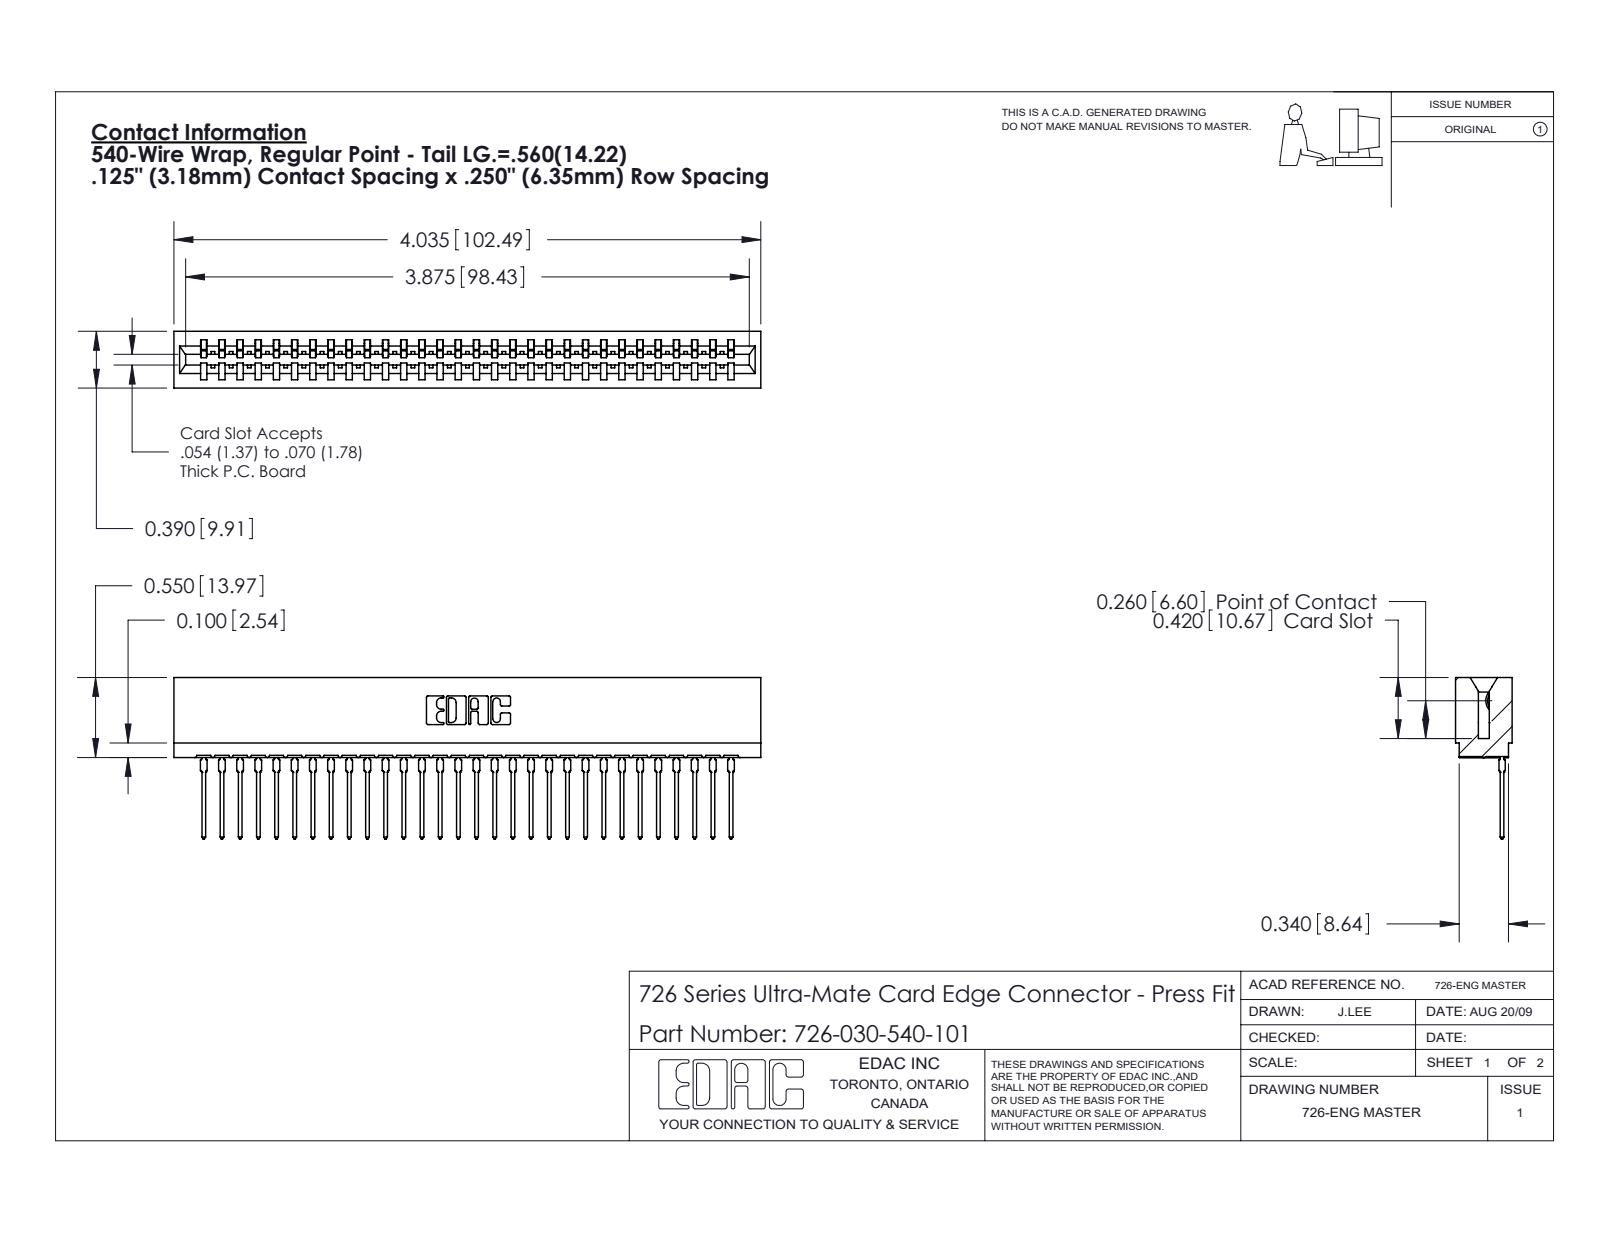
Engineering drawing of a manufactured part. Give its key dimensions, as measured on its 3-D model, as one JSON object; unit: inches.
{"part_name": "726 Part_.515 Slot Depth - 01; 746-292-001_540; 726-030-540-101", "step_written_by": "SolidWorks 2020 (CONFIG_CONTROL_DESIGN)", "units": "inches", "bodies": {"solids": 31, "faces": 3337, "planar": 1945, "cylindrical": 612, "other": 780}, "overall_size": [4.035, 1.109, 0.39], "volume_in3": 0.567, "surface_area_in2": 22.26, "partial_cylinders_radius": [[0.021, 60], [0.015, 31], [0.01, 22], [0.007, 6], [0.031, 6], [0.005, 4], [0.011, 4], [0.026, 3]], "face_to_face_distances": [0.057, 0.333, 0.39, 0.25, 0.025, 0.307, 0.083, 0.5, 0.75, 0.275]}
